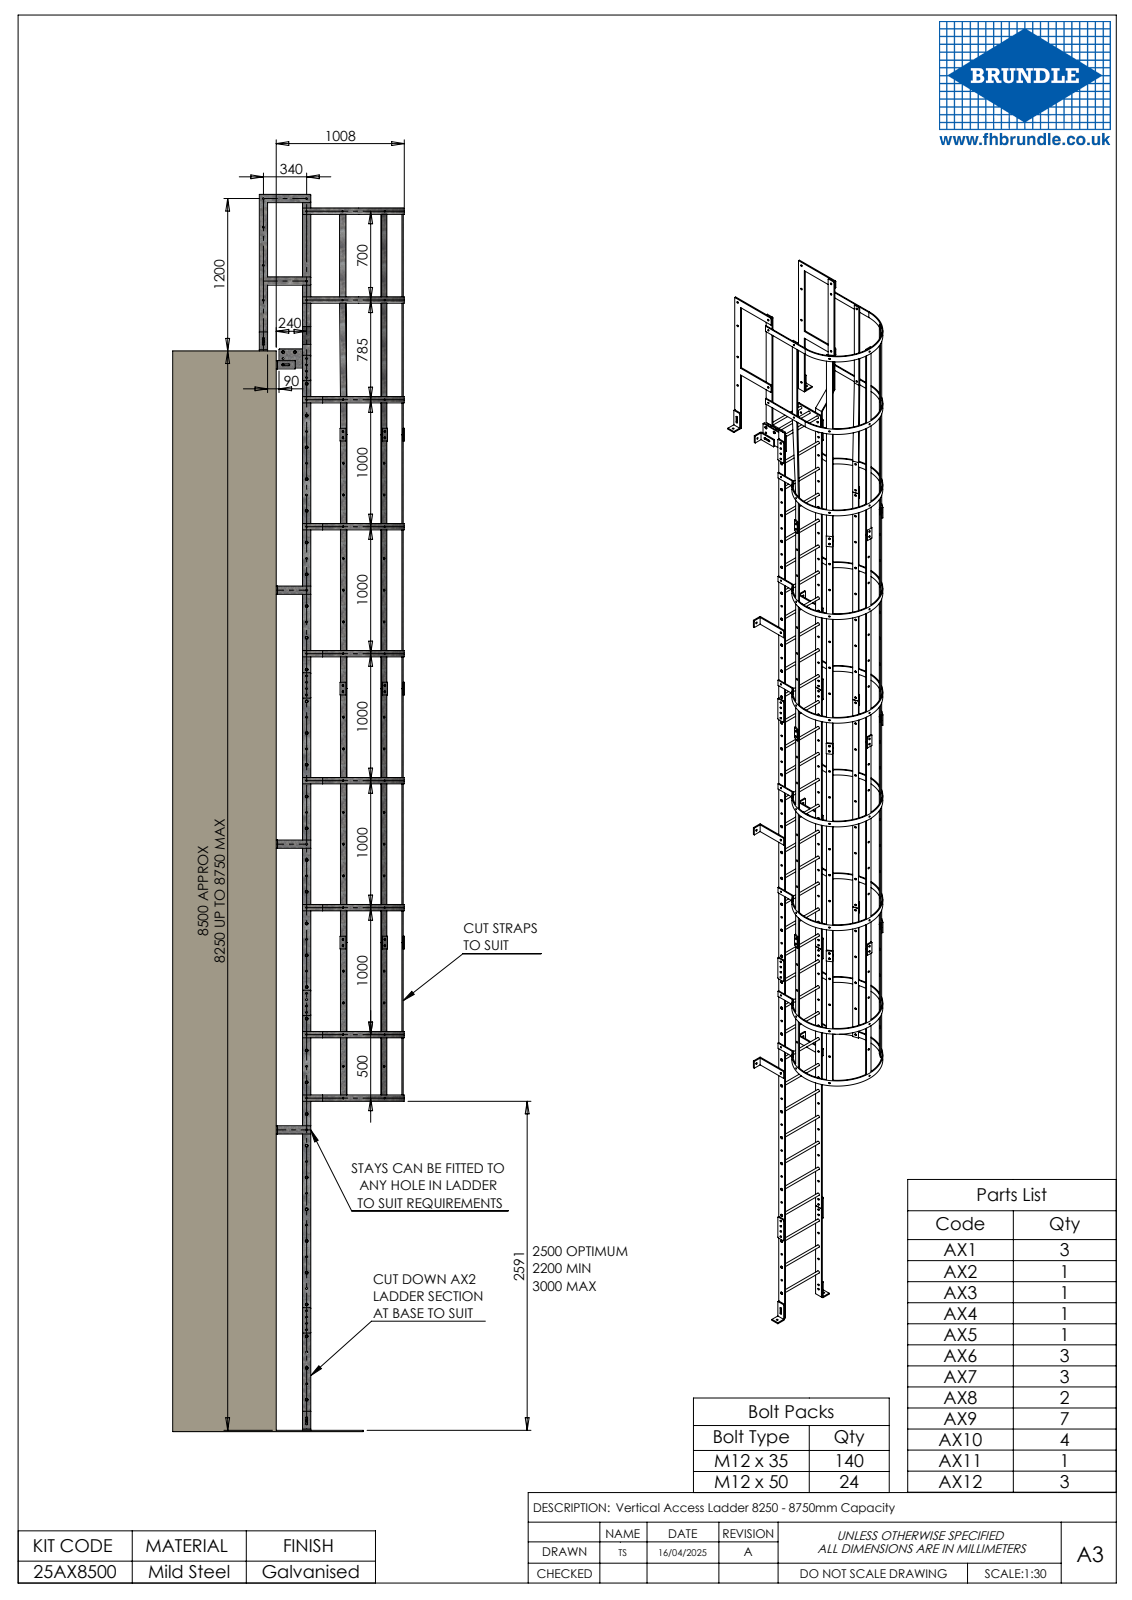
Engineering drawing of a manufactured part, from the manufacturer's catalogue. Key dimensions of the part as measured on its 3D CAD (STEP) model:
Part name (STEP PRODUCT): 25AX12; 25AX11_Bent LHS; 25AX11_MirrorBent LHS; 25AX6 (+8 more)
STEP written by: SolidWorks 2023 (CONFIG_CONTROL_DESIGN)
Units: millimetres
Bodies: 114 solids, 1764 faces (622 planar, 1134 cylindrical, 8 other)
Overall size (bounding box): 9733 × 1142 × 870
Volume: 48 670 000 mm³ · Surface area: 12 060 000 mm²
Round holes (diameter × count): ⌀15 ×207, ⌀12 ×52, ⌀20 ×36, ⌀14 ×6, ⌀700 ×1
Partial cylindrical surfaces — rounded edges, fillets, slot ends (radius × count): R5 ×26, R2 ×6, R7 ×6, R10 ×6, R358 ×2, R350 ×1
Main face-to-face distances: 10, 410, 140, 560, 420, 150, 550, 400, 20, 0.5
Hole centre spacings: 250, 1000, 500, 750, 1250, 2000, 1500, 1750
